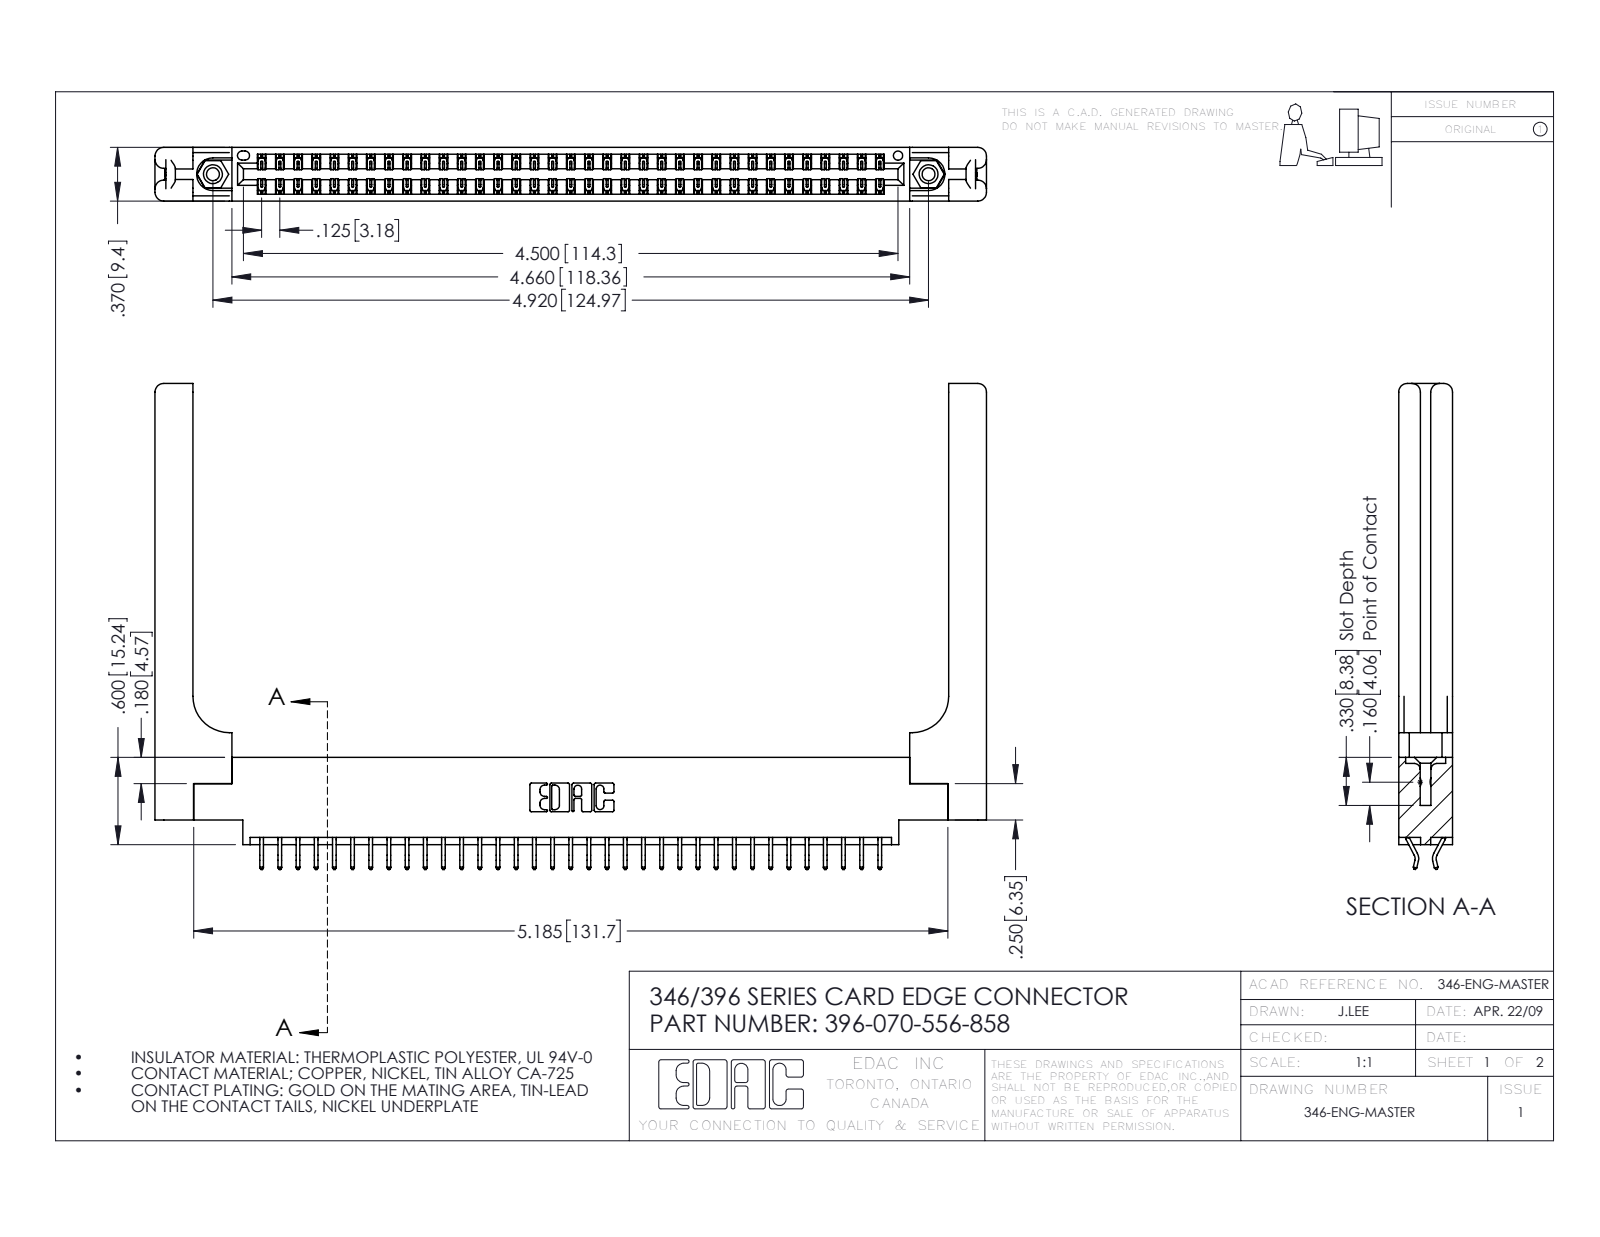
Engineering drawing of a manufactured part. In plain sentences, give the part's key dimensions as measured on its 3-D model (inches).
The part is named "345-250-001_345-250-001-102; 346 Part_0.170 Offset - 0.156 Dia-TH; 346-220-058_345-220-058; 345-292-001_556 Tail (+1 more)". Its 3-D file was written by "SolidWorks 2016 (CONFIG_CONTROL_DESIGN)". It is 75 solids with 4442 faces: 2958 planar, 1424 cylindrical and 60 other. Overall it measures 5.716 by 3.34 by 0.37 inches. Its volume is 1.308 cubic inches and its surface area 37.43 square inches. Round holes: 2 of diameter 0.089, 2 of diameter 0.125, 2 of diameter 0.156, 1 of diameter 0.064. Round bosses or shafts: 2 of diameter 0.155. Partial cylindrical surfaces (rounded edges, fillets, slot ends): 105 of radius 0.006, 22 of radius 0.01, 16 of radius 0.06, 6 of radius 0.007, 6 of radius 0.031, 3 of radius 0.026, 2 of radius 0.01, 2 of radius 0.014. The main face-to-face distances are 0.37, 0.048, 0.322, 0.072, 0.148, 0.15, 0.25, 0.025, 0.298, 0.275. The hole center spacings are 0.246, 4.711, 4.92.
